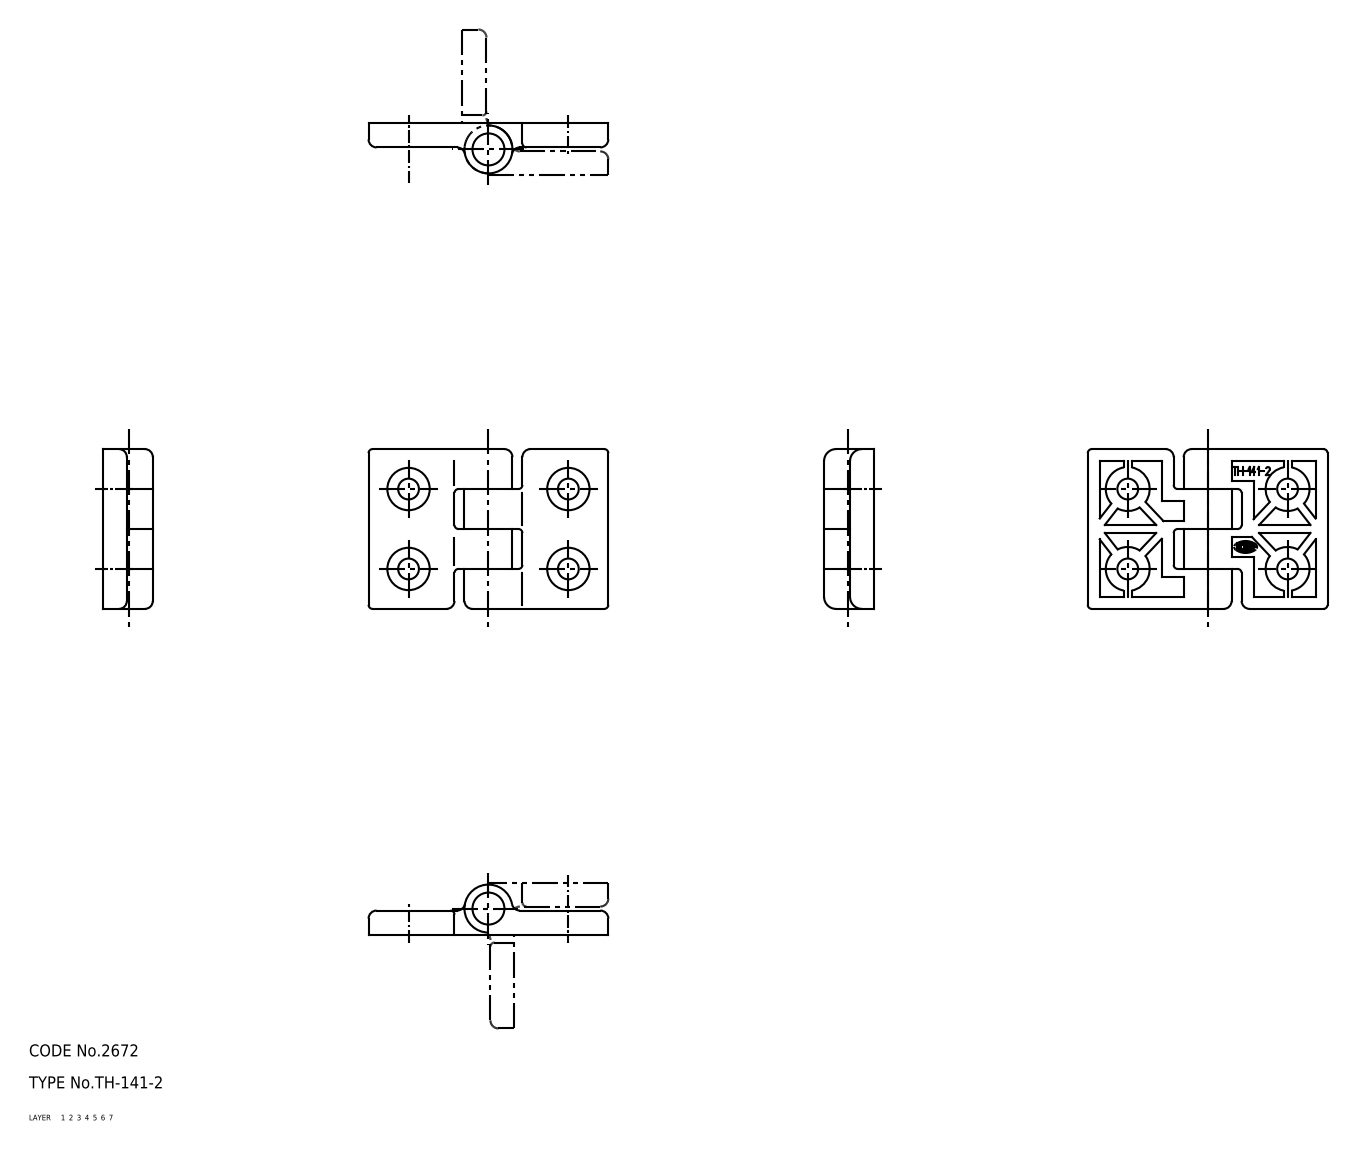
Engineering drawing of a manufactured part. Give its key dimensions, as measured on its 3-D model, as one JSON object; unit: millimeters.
{"part_name": "cap; hinge pieces; shaft; TH_141_2_27706_36", "step_written_by": "CADfix (AUTOMOTIVE_DESIGN)", "units": "millimeters", "bodies": {"solids": 5, "faces": 198, "planar": 0, "cylindrical": 0, "other": 198}, "overall_size": [60, 40, 12.5], "volume_mm3": 12617, "surface_area_mm2": 11171}
